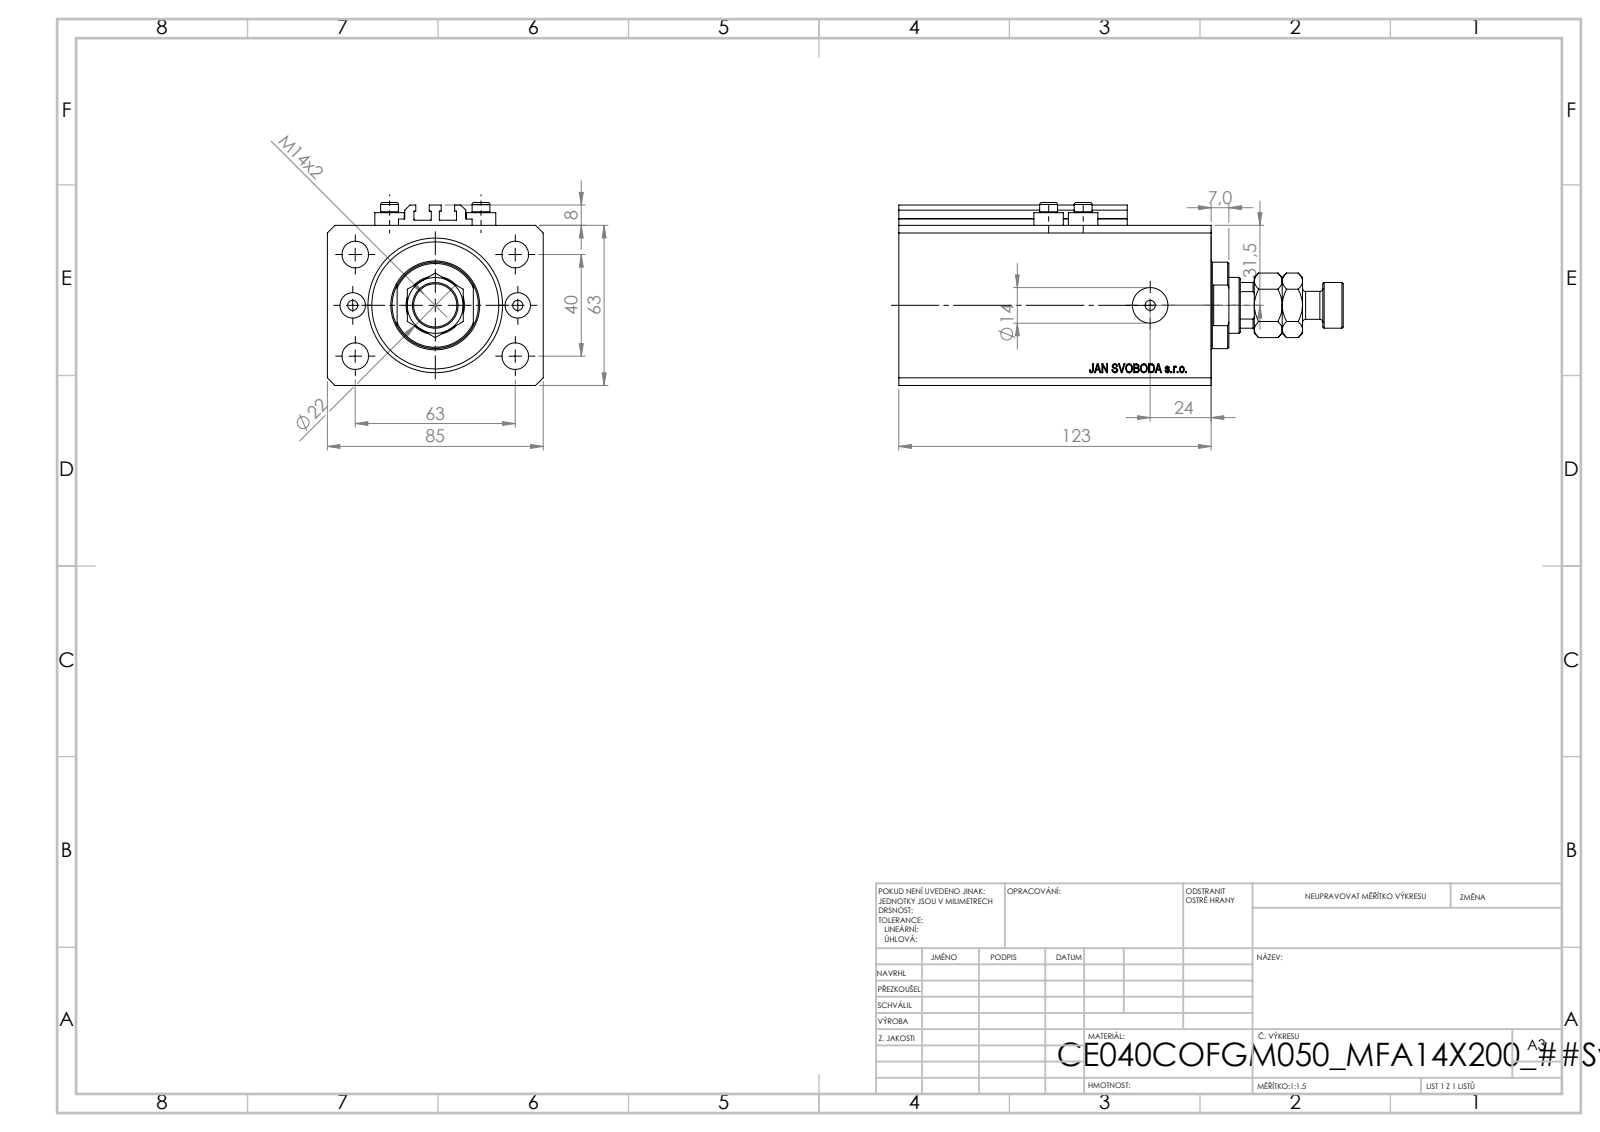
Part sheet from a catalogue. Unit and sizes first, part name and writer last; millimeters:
Units: millimetres
Overall size (bounding box): 175 × 85 × 72
Round holes (diameter × count): ⌀4 ×8, ⌀10.5 ×4, ⌀10 ×2, ⌀14 ×2, ⌀12.5 ×1, ⌀22 ×1, ⌀40 ×1, ⌀53 ×1
Round bosses / shafts (diameter × count): ⌀11.6 ×4, ⌀7 ×4, ⌀34 ×1, ⌀18 ×1, ⌀11 ×1
Partial cylindrical surfaces — rounded edges, fillets, slot ends (radius × count): R0.2 ×10, R10.5 ×1
Main face-to-face distances: 63, 85, 123, 17, 106, 11.4, 94.6, 111.6, 10, 2.5
Hole centre spacings: 20.02, 37.31, 67.05, 13.6, 32.5, 36, 38.48, 40
Volume: 598 032 mm³ · Surface area: 116 918 mm²
Bodies: 9 solids, 1086 faces (520 planar, 90 cylindrical, 476 other)
Part name (STEP PRODUCT): MFA; V250CE_C_Body; V250CE_VC_C; ALLEN BOLT V250CE (+1 more)
STEP written by: SolidWorks 2019 (CONFIG_CONTROL_DESIGN)
